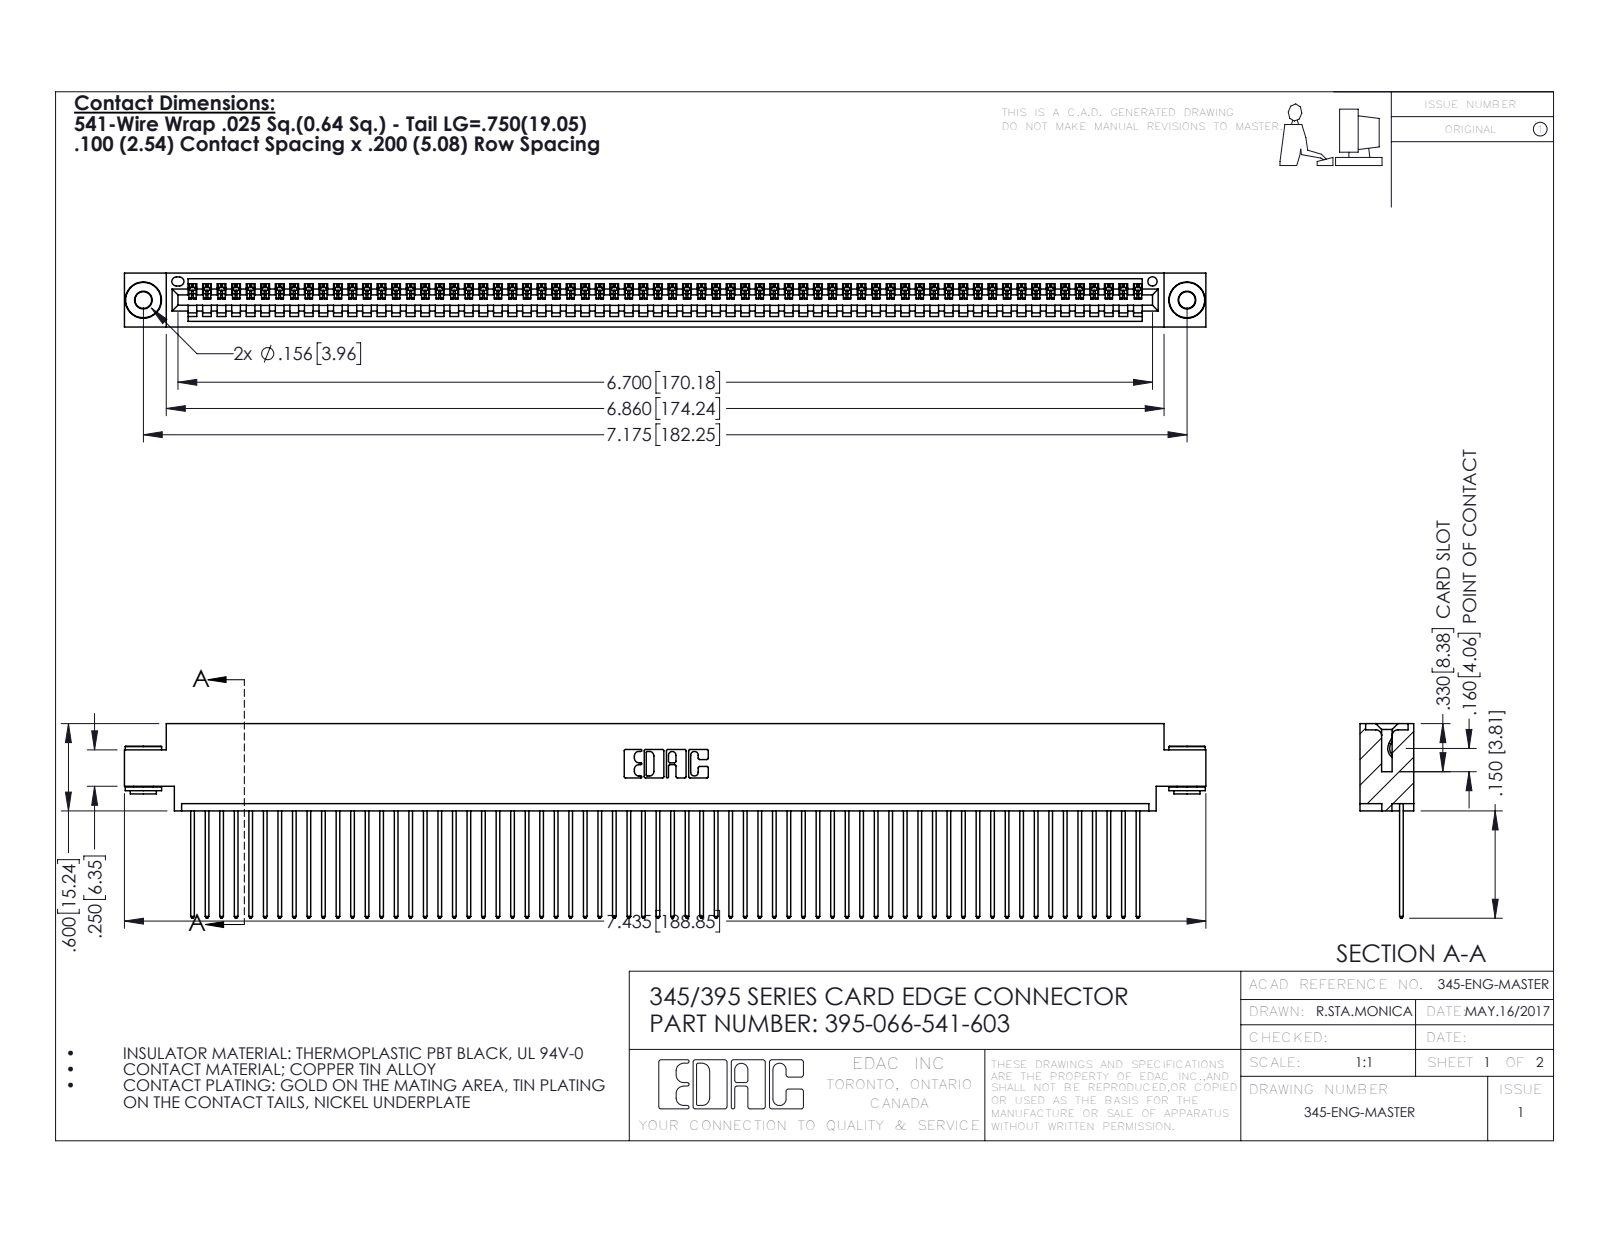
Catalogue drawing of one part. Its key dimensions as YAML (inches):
part_name: "345-292-001_345-293-141; 395-066-541-603; 345 Part_0.170 Offset - 0.156 Dia-TH; 345-250-002_345-250-002-102"
step_written_by: "SolidWorks 2016 (CONFIG_CONTROL_DESIGN)"
units: inches
bodies: {solids: 69, faces: 3996, planar: 2734, cylindrical: 1254, other: 8}
overall_size: [7.435, 1.337, 0.37]
volume: 1.114
surface_area: 40.63
round_holes:
  - {diameter: 0.116, count: 2}
  - {diameter: 0.156, count: 2}
  - {diameter: 0.064, count: 1}
round_bosses_or_shafts:
  - {diameter: 0.25, count: 2}
  - {diameter: 0.18, count: 2}
  - {diameter: 0.136, count: 2}
partial_cylinders:
  - {radius: 0.006, count: 132}
  - {radius: 0.01, count: 132}
  - {radius: 0.01, count: 22}
  - {radius: 0.007, count: 6}
  - {radius: 0.031, count: 6}
  - {radius: 0.026, count: 3}
  - {radius: 0.031, count: 2}
  - {radius: 0.04, count: 2}
face_to_face_distances: [0.072, 0.298, 0.098, 0.272, 0.025, 0.37, 0.2, 0.225, 0.175, 0.149]
hole_center_spacings: [0.27, 6.939, 7.175]
